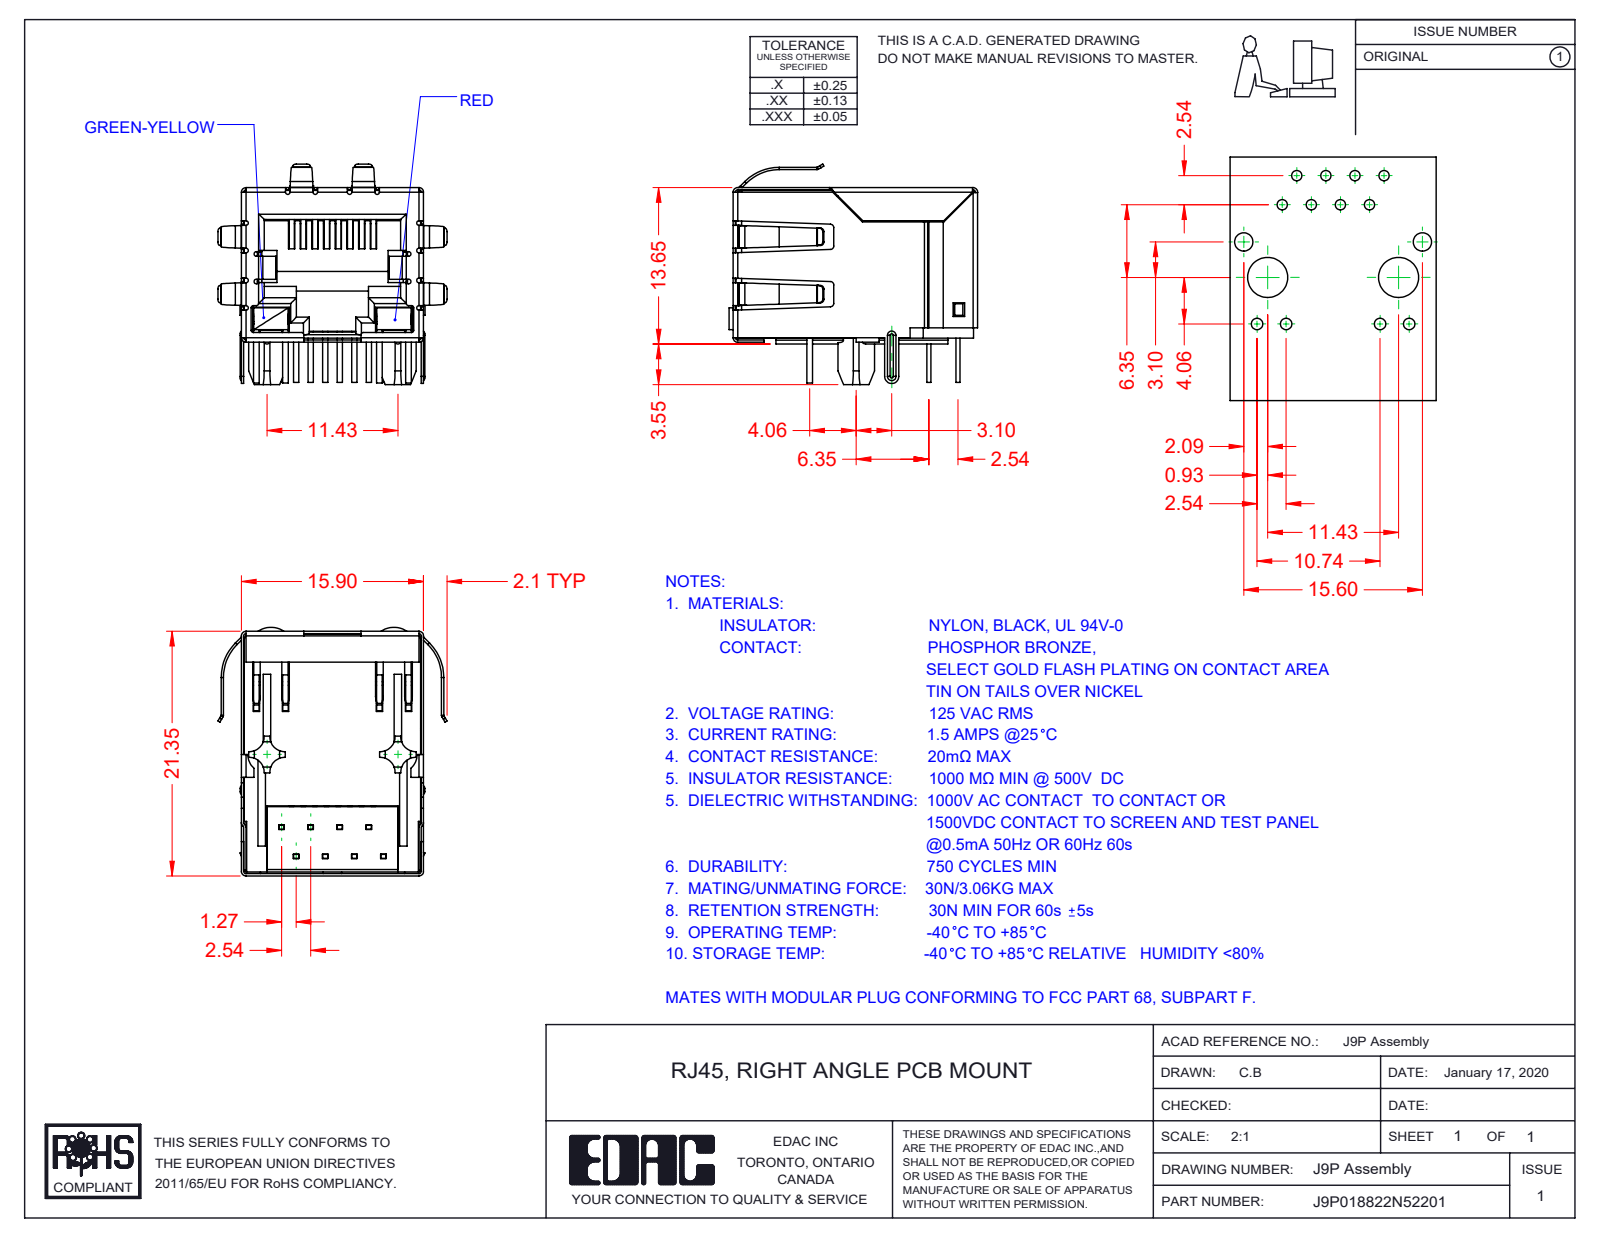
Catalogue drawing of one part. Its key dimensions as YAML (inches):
part_name: "9P-LED Contact Lock; J9P018822N52202; 9P-LED Shield; 9P-LED LED RH_2-Red (+4 more)"
step_written_by: "SolidWorks 2016 (CONFIG_CONTROL_DESIGN)"
units: inches
bodies: {solids: 13, faces: 1474, planar: 1042, cylindrical: 338, other: 94}
overall_size: [0.854, 0.787, 0.758]
volume: 0.164
surface_area: 11.65
partial_cylinders:
  - {radius: 0.008, count: 39}
  - {radius: 0.02, count: 22}
  - {radius: 0.012, count: 20}
  - {radius: 0.016, count: 16}
  - {radius: 0.051, count: 8}
  - {radius: 0.009, count: 5}
  - {radius: 0.004, count: 4}
  - {radius: 0.012, count: 4}
face_to_face_distances: [0.608, 0.618, 0.616, 0.014, 0.021, 0.61, 0.487, 0.024, 0.055, 0.023]
